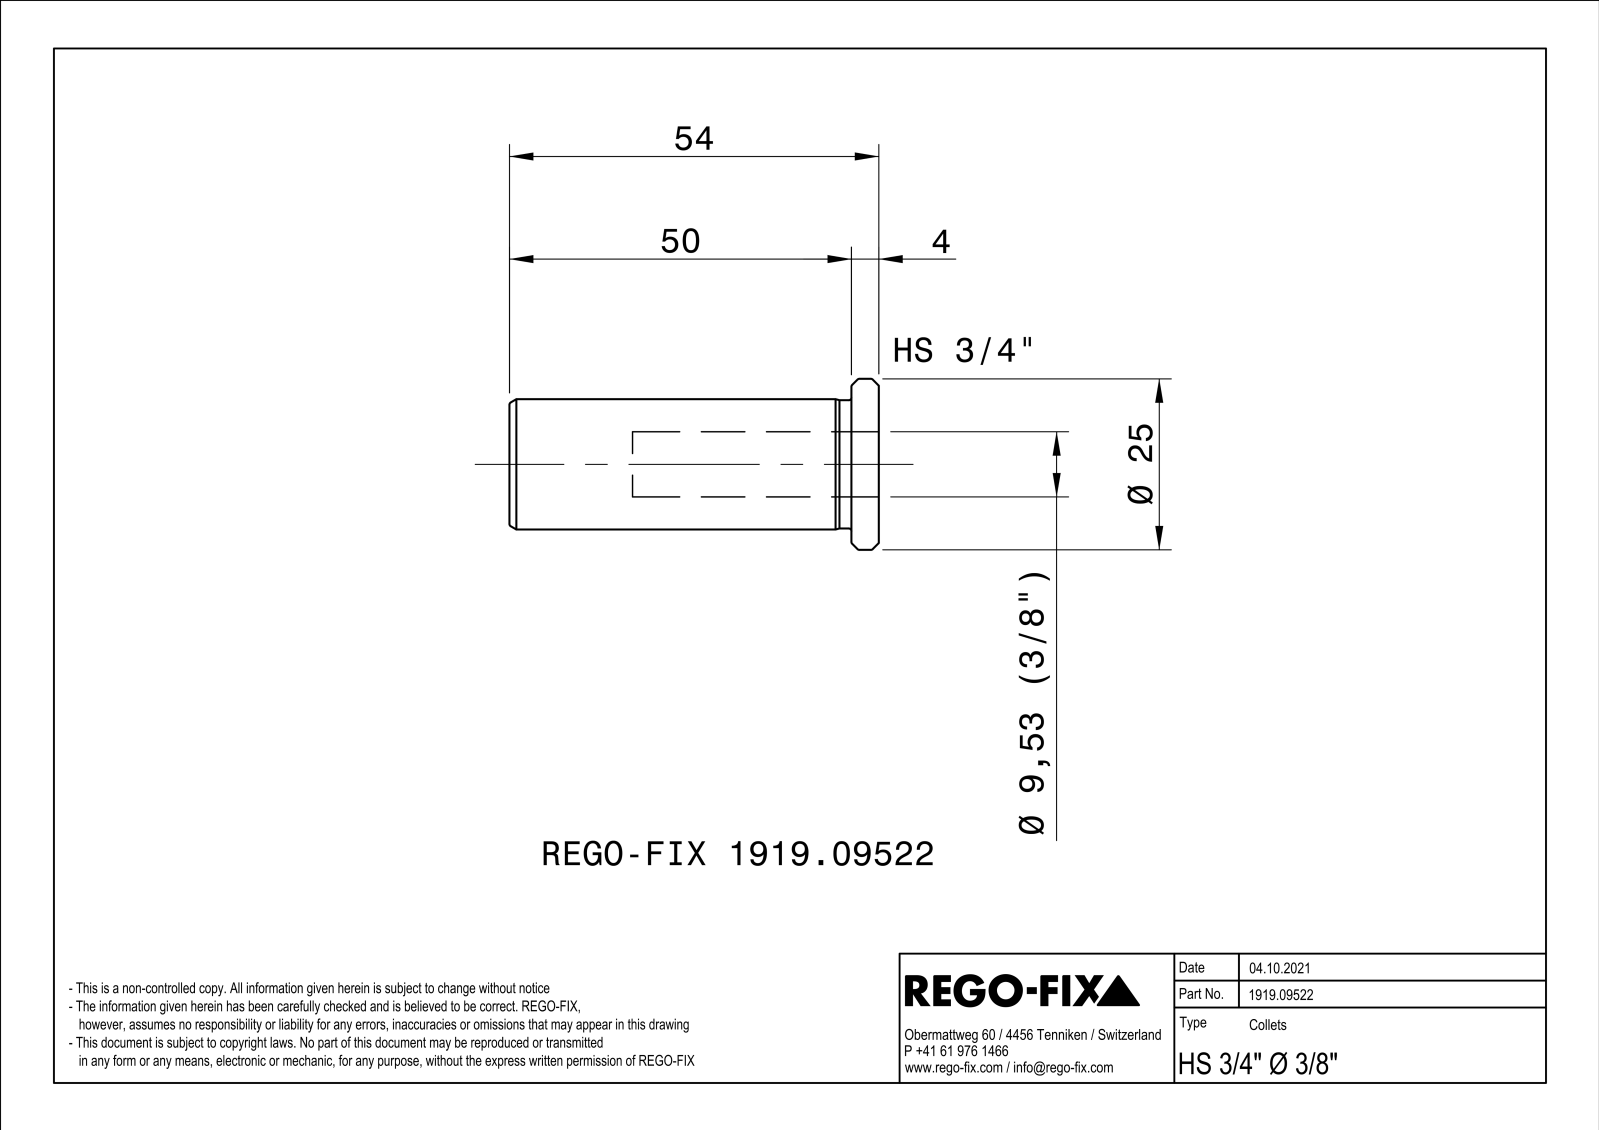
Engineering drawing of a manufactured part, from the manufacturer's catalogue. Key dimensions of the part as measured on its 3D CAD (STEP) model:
Part name (STEP PRODUCT): NOCUT
STEP written by: SIEMENS PLM Software Solid Edge ST10 (AUTOMOTIVE_DESIGN)
Units: millimetres
Bodies: 1 solid, 72 faces (22 planar, 12 cylindrical, 38 other)
Overall size (bounding box): 54 × 24.98 × 24.98
Volume: 9 777 mm³ · Surface area: 7 074 mm²
Round holes (diameter × count): ⌀9.53 ×1, ⌀10.5 ×1, ⌀16.5 ×1
Round bosses / shafts (diameter × count): ⌀25 ×1, ⌀19.05 ×1, ⌀18.75 ×1
Main face-to-face distances: 1, 4, 54, 50
